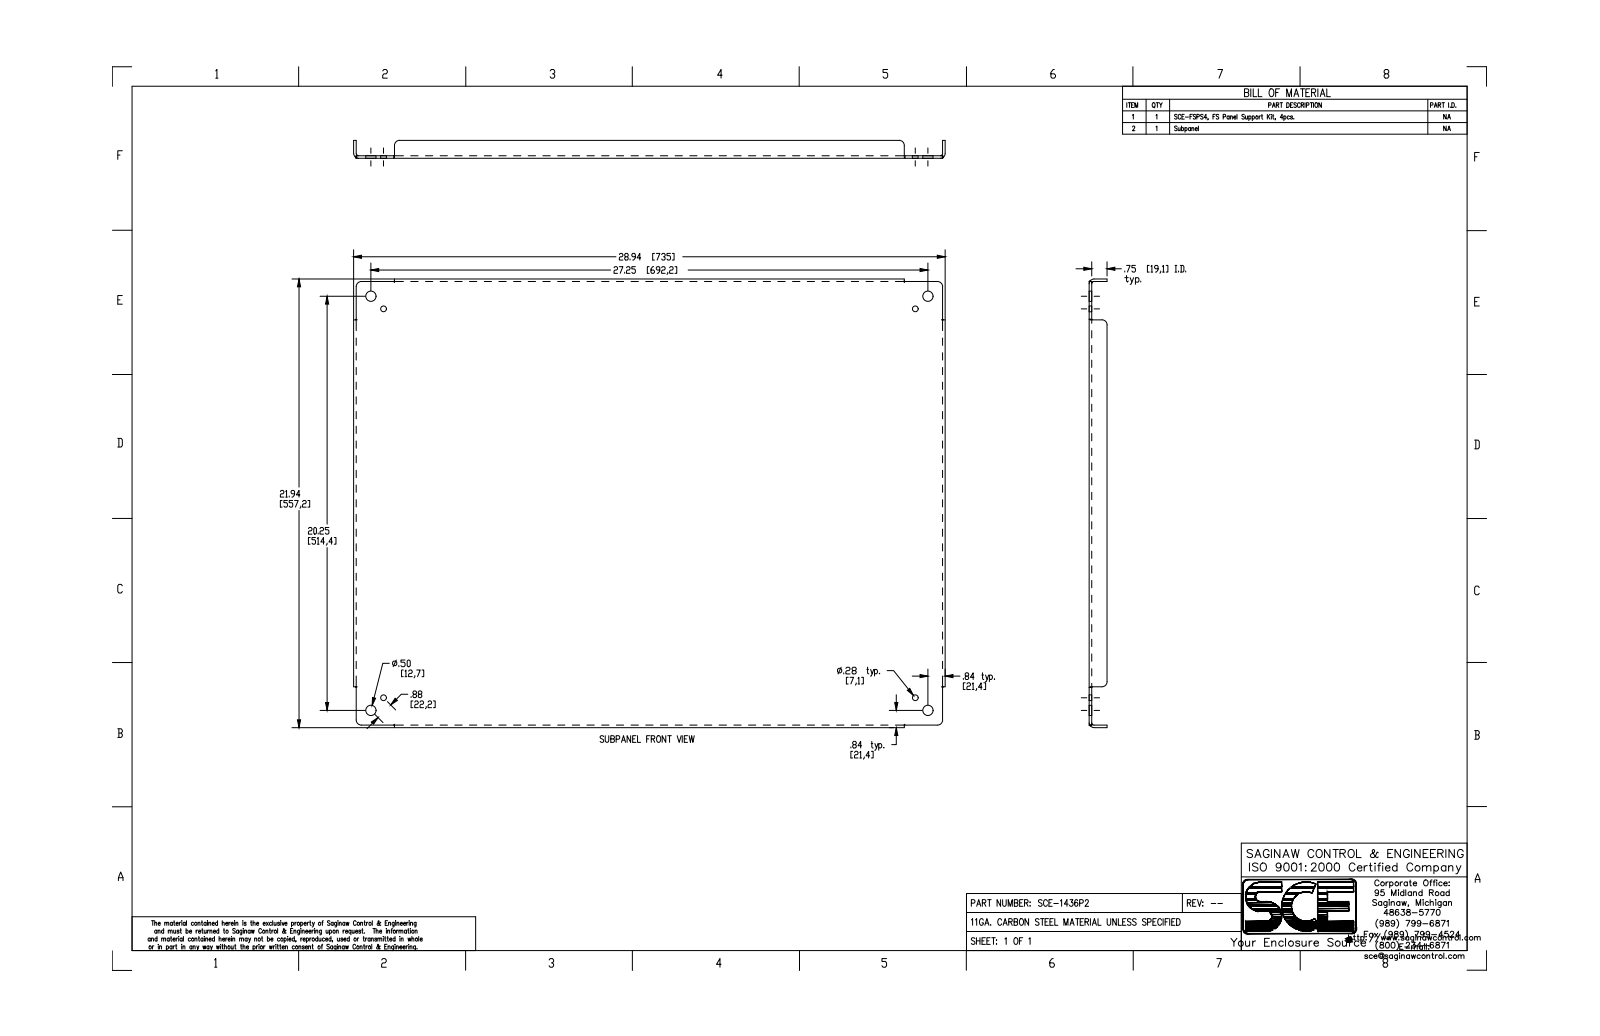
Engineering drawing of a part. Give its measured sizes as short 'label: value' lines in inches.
name: SCE-1436P2
written by: SolidWorks 2019 (CONFIG_CONTROL_DESIGN)
unit: in
bodies: 1 solid, 82 faces (30 planar, 28 cylindrical, 24 other)
size: 28.938 × 21.938 × 0.875
volume: 86.2 in³; area: 1 394 in²
holes: 4× ⌀0.281, 4× ⌀0.5
rounds: 8× R0.25, 4× R0.112, 4× R0.237
face distances: 0.125, 0.125, 21.813, 28.813, 21.687, 21.938, 28.687, 28.938, 0.75, 0.875
hole spacings: 0.875, 19.641, 26.638, 33.085, 19.013, 20.25, 26.013, 27.25
